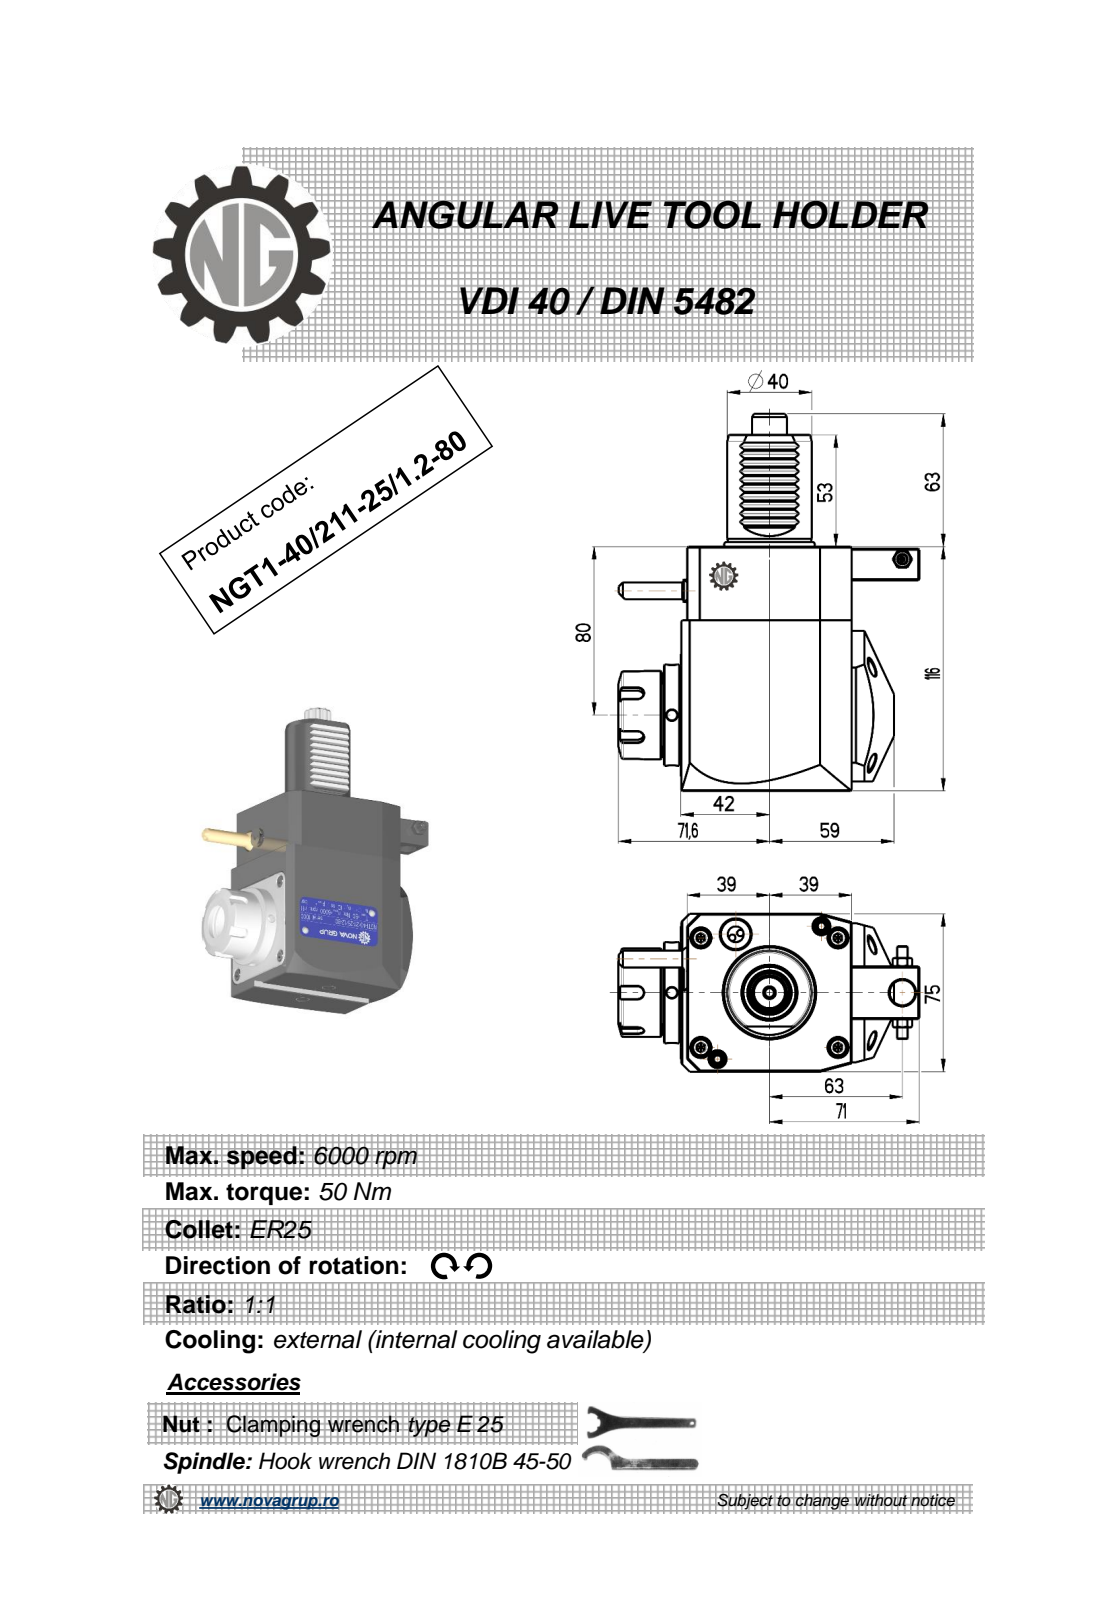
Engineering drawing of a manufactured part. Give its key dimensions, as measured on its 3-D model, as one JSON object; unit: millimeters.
{"part_name": "NGT1_40_211_25_1_2_80", "step_written_by": "PRO/ENGINEER BY PARAMETRIC TECHNOLOGY CORPORATION, 2010280 (CONFIG_CONTROL_DESIGN)", "units": "millimeters", "bodies": {"solids": 1, "faces": 474, "planar": 184, "cylindrical": 124, "other": 166}, "overall_size": [179, 142.6, 76.6], "volume_mm3": 852326, "surface_area_mm2": 68997, "round_holes": [[5, 3], [4.2, 2], [3, 1], [9.5, 1], [12, 1], [20.3, 1]], "round_bosses_or_shafts": [[48, 1], [42, 1], [40, 1], [37.5, 1], [33, 1], [11.2, 1], [8.96, 1], [8, 1]], "partial_cylinders_radius": [[3.03, 18], [0.26, 12], [0.3, 10], [0.22, 6], [3, 5], [0.5, 1], [6.75, 1], [8.22, 1]], "face_to_face_distances": [75, 116, 81, 3, 78, 2.8, 80.8, 25, 7.5, 11], "hole_center_spacings": [20.93, 46.25, 61.13, 63, 72.5, 109.25, 131.95]}
